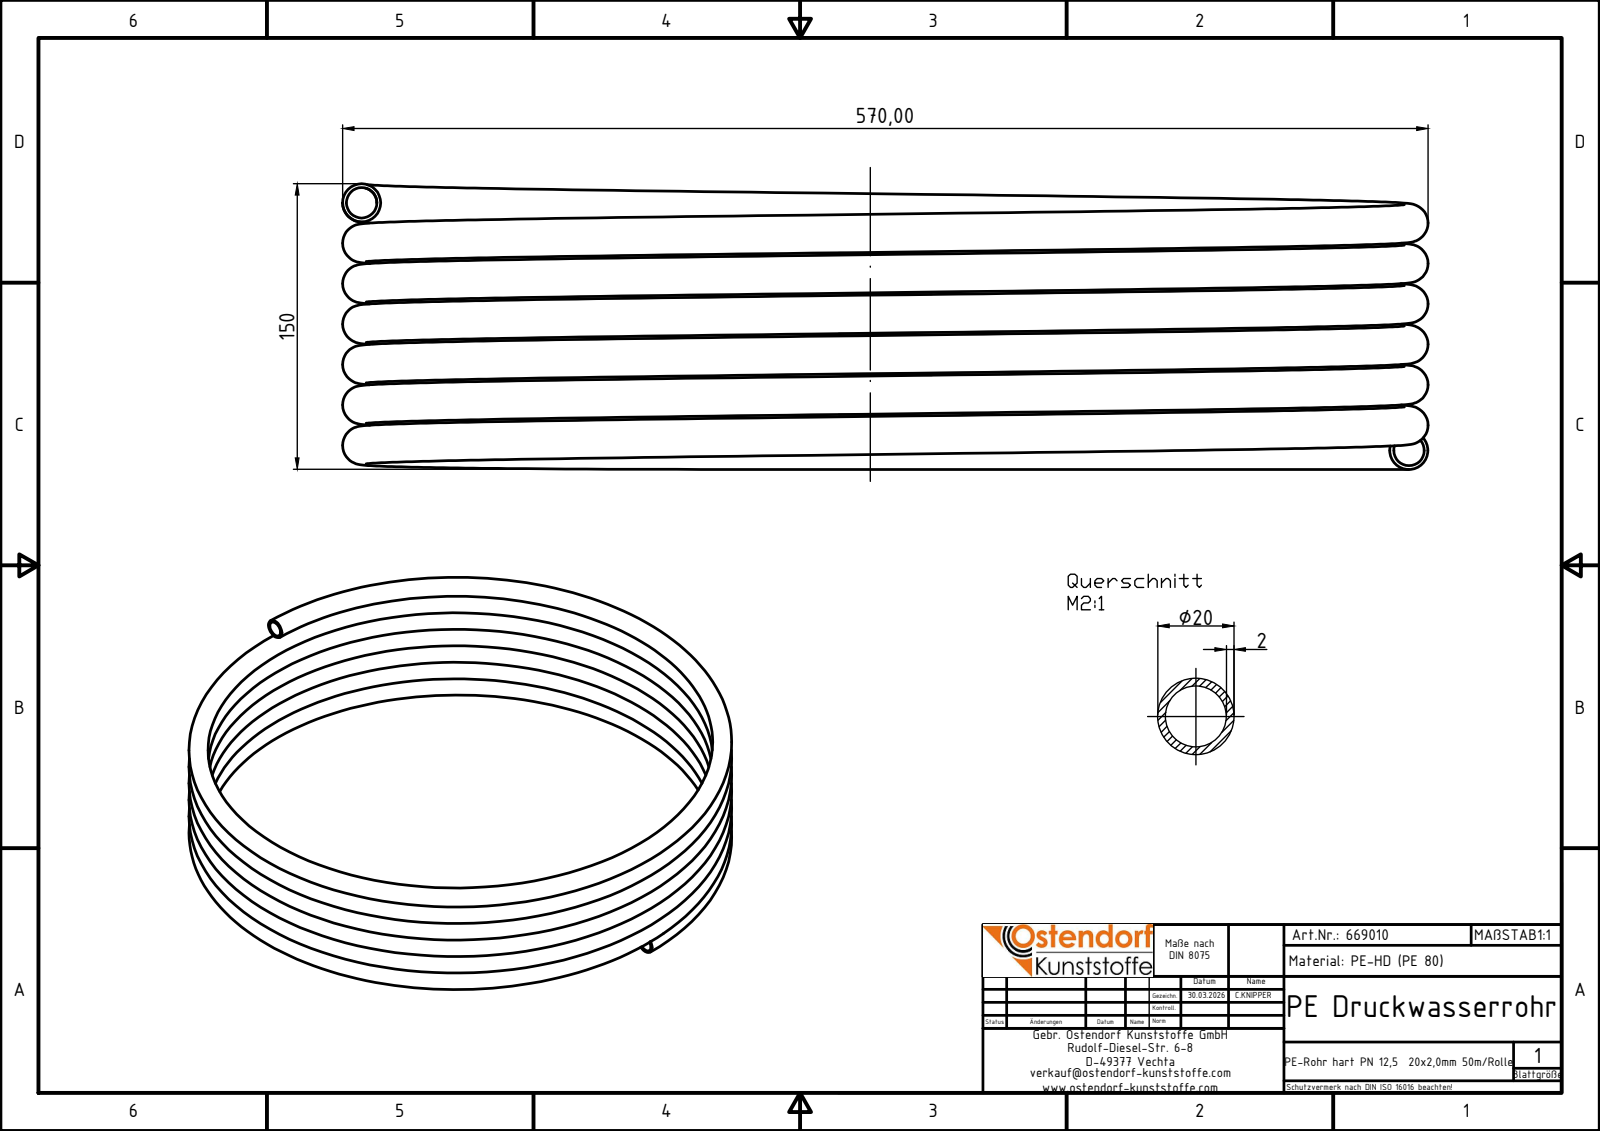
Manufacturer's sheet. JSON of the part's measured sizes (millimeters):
{"part_name": "669010z", "step_written_by": "Autodesk Inventor 2024 (AUTOMOTIVE_DESIGN)", "units": "millimeters", "bodies": {"solids": 1, "faces": 7, "planar": 3, "cylindrical": 0, "other": 4}, "overall_size": [570.01, 570.01, 150.03], "volume_mm3": 1262000, "surface_area_mm2": 1255000}
